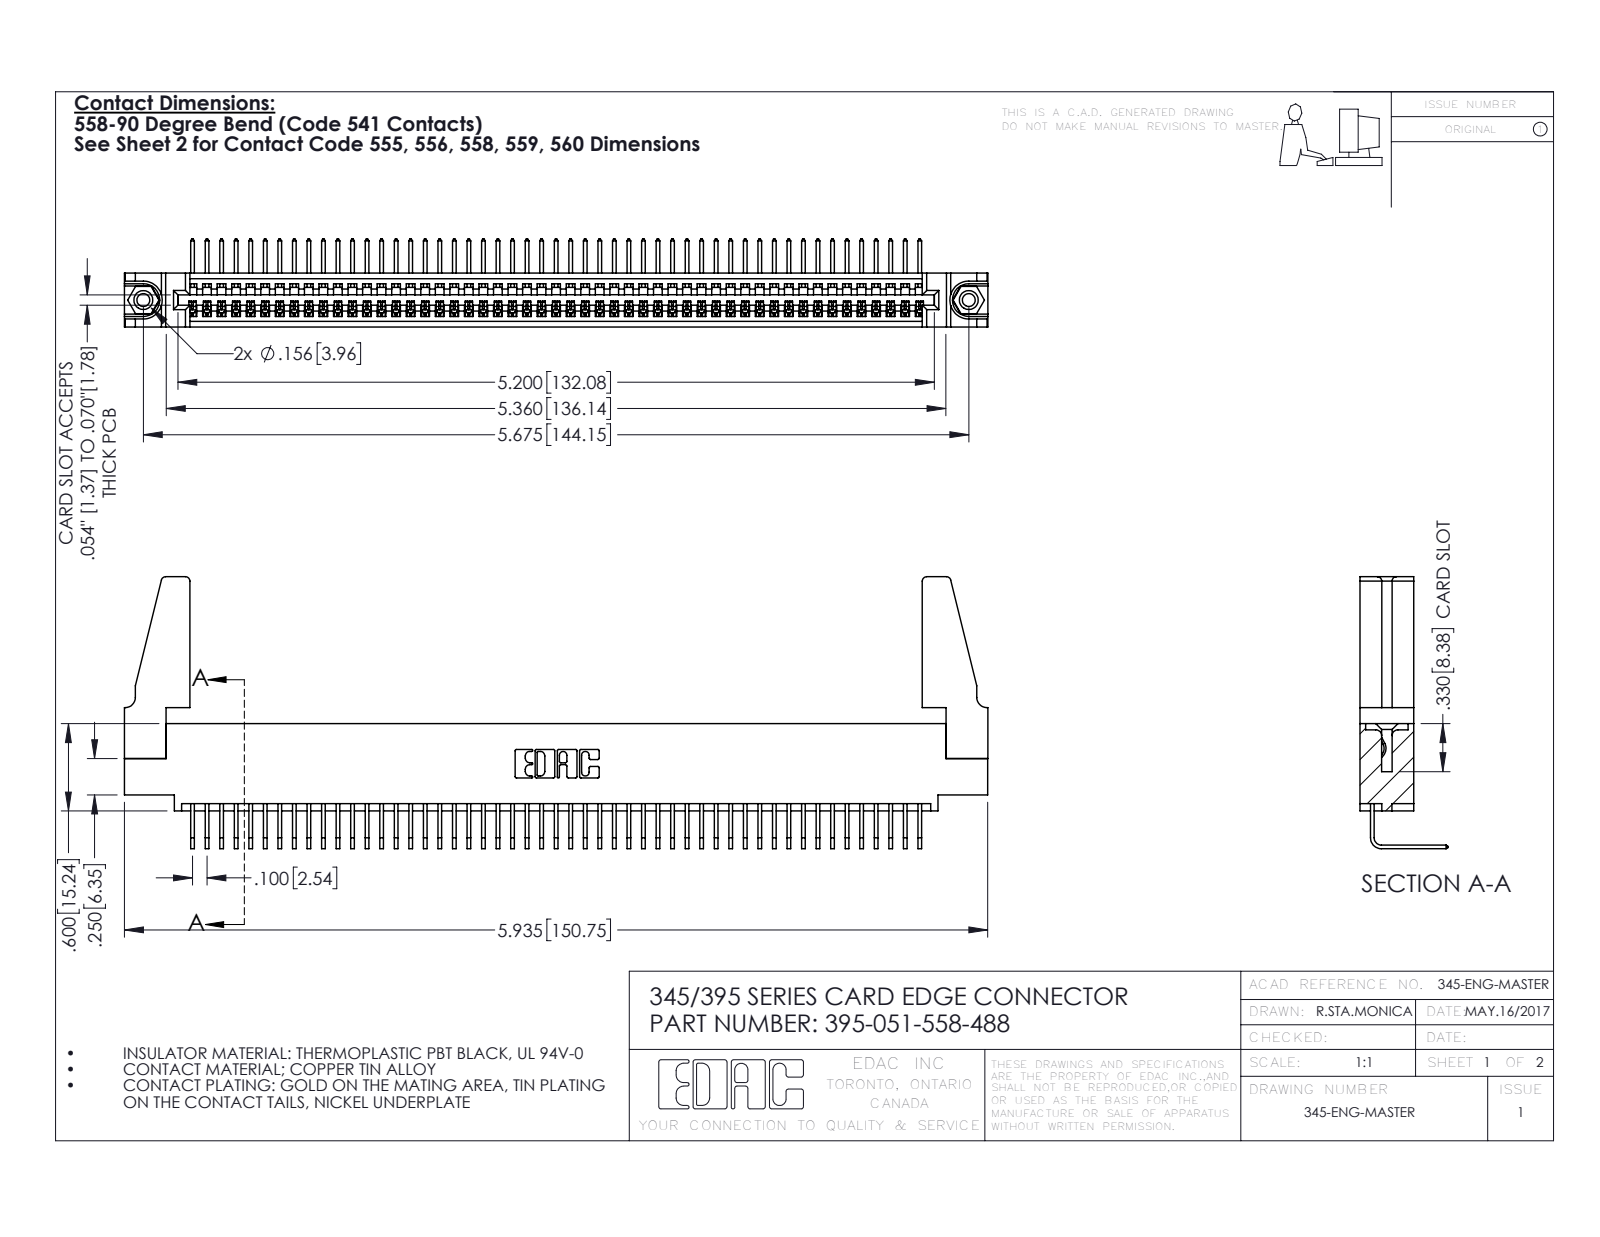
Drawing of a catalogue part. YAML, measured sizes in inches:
part_name: "345-220-078_345-220-088; 395-051-558-488; 345-250-001_345-250-001-102; 345 Part_0.110 Offset - 0.156 Dia-TH (+1 more)"
step_written_by: "SolidWorks 2016 (CONFIG_CONTROL_DESIGN)"
units: inches
bodies: {solids: 56, faces: 3314, planar: 2298, cylindrical: 1000, other: 16}
overall_size: [5.936, 1.869, 0.605]
volume: 1.083
surface_area: 36.56
round_holes:
  - {diameter: 0.089, count: 2}
  - {diameter: 0.125, count: 2}
  - {diameter: 0.156, count: 2}
  - {diameter: 0.064, count: 1}
round_bosses_or_shafts:
  - {diameter: 0.155, count: 2}
partial_cylinders:
  - {radius: 0.006, count: 102}
  - {radius: 0.01, count: 22}
  - {radius: 0.03, count: 8}
  - {radius: 0.007, count: 6}
  - {radius: 0.031, count: 6}
  - {radius: 0.026, count: 3}
  - {radius: 0.031, count: 2}
  - {radius: 0.04, count: 2}
face_to_face_distances: [0.072, 0.298, 0.37, 0.2, 0.098, 0.272, 0.025, 0.225, 0.149, 0.072]
hole_center_spacings: [0.27, 5.439, 5.675]
